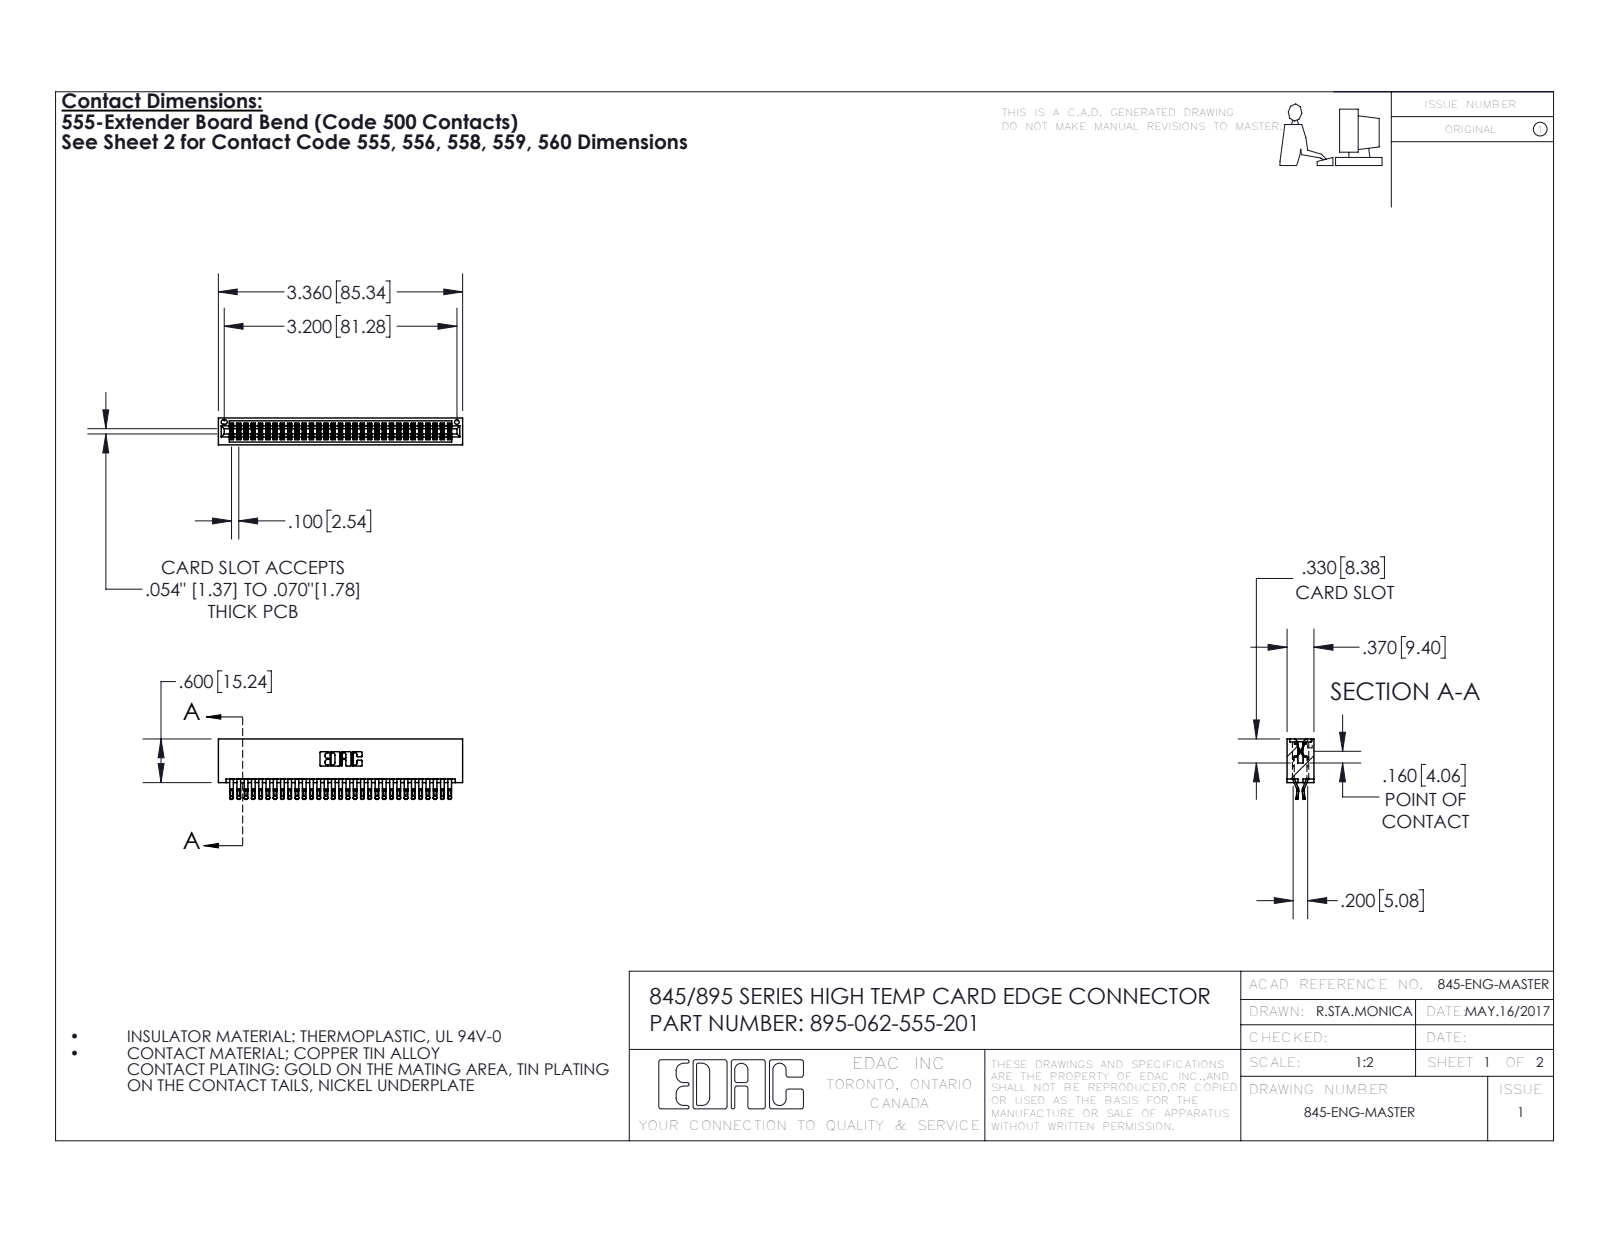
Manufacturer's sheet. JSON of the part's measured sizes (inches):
{"part_name": "395-062-555-201; 345-292-001_555 Tail; 345 Part_No Mounting Lugs", "step_written_by": "SolidWorks 2016 (CONFIG_CONTROL_DESIGN)", "units": "inches", "bodies": {"solids": 63, "faces": 3590, "planar": 1998, "cylindrical": 1592, "other": 0}, "overall_size": [3.36, 0.832, 0.37], "volume_in3": 0.548, "surface_area_in2": 21.69, "round_holes": [[0.064, 1]], "partial_cylinders_radius": [[0.016, 155], [0.02, 124], [0.006, 93], [0.01, 22], [0.007, 6], [0.031, 6], [0.026, 3], [0.01, 2]], "face_to_face_distances": [0.298, 0.072, 0.2, 0.025, 0.37, 0.098, 0.272, 0.225, 0.175, 0.149]}
